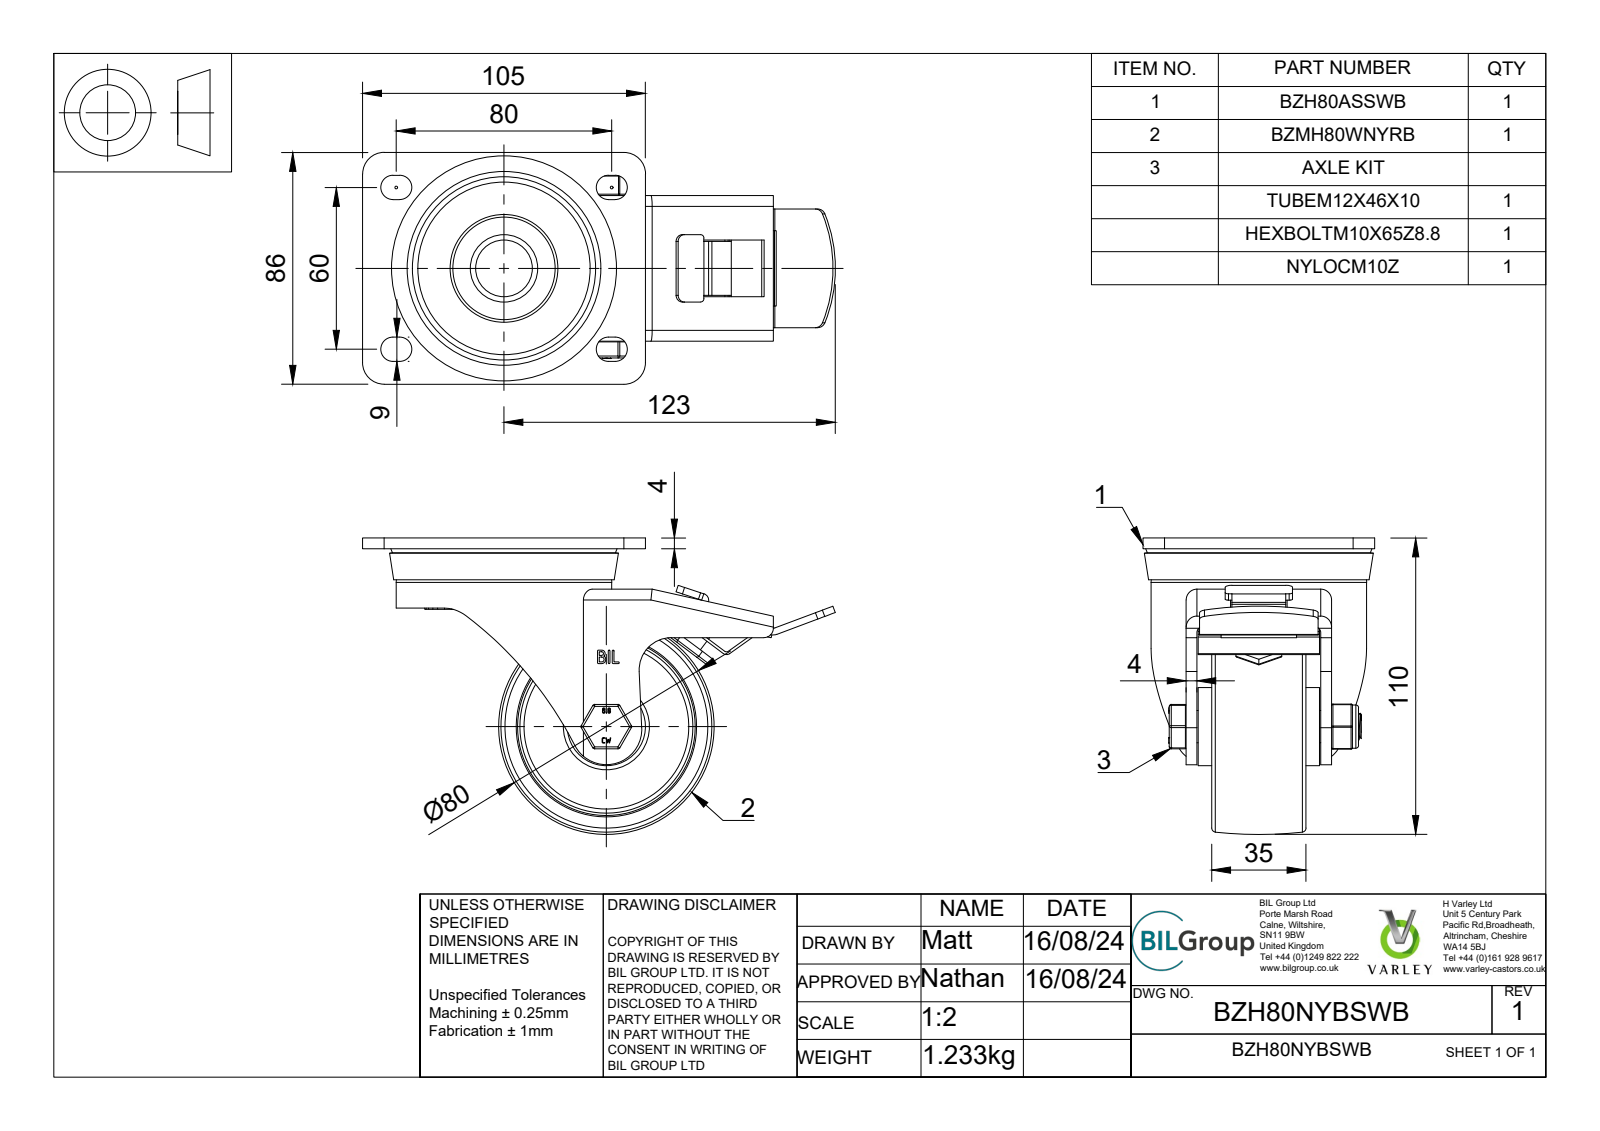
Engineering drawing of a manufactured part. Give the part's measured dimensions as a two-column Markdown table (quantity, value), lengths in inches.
| quantity | value |
| --- | --- |
| part name | BZH80NYBSWB v3; BZH80ASSWB v1; ZINC PLATED, PRESSED STEEL TOP PLATE; ZINC PLATED, PRESSED STEEL FORKS (+8 more) |
| STEP written by | Autodesk Translation Framework v13.14.0.145 (AUTOMOTIVE_DESIGN) |
| units | inches |
| bodies | 21 solids, 752 faces (376 planar, 268 cylindrical, 108 other) |
| overall size | 6.909 × 4.331 × 3.386 |
| volume | 14.67 in³ |
| surface area | 198.1 in² |
| round holes (diameter × count) | 0.315 × 1, 0.394 × 1, 0.402 × 1, 0.472 × 1, 0.488 × 1, 0.492 × 1, 0.787 × 1, 0.984 × 1, 1.26 × 1, 2.835 × 1 |
| round bosses / shafts (diameter × count) | 0.148 × 8, 3.15 × 1, 2.323 × 1, 1.22 × 1, 1.142 × 1, 0.787 × 1, 0.768 × 1, 0.63 × 1 |
| partial cylindrical surfaces (radius × count) | 0.02 × 18, 0.03 × 18, 0.079 × 10, 0.177 × 8, 0.157 × 5, 0.098 × 4, 0.118 × 4, 0.315 × 4 |
| main face-to-face distances | 0.157, 0.295, 0.118, 0.039, 0.453, 1.004, 0.02, 0.748, 0.846, 0.138 |
